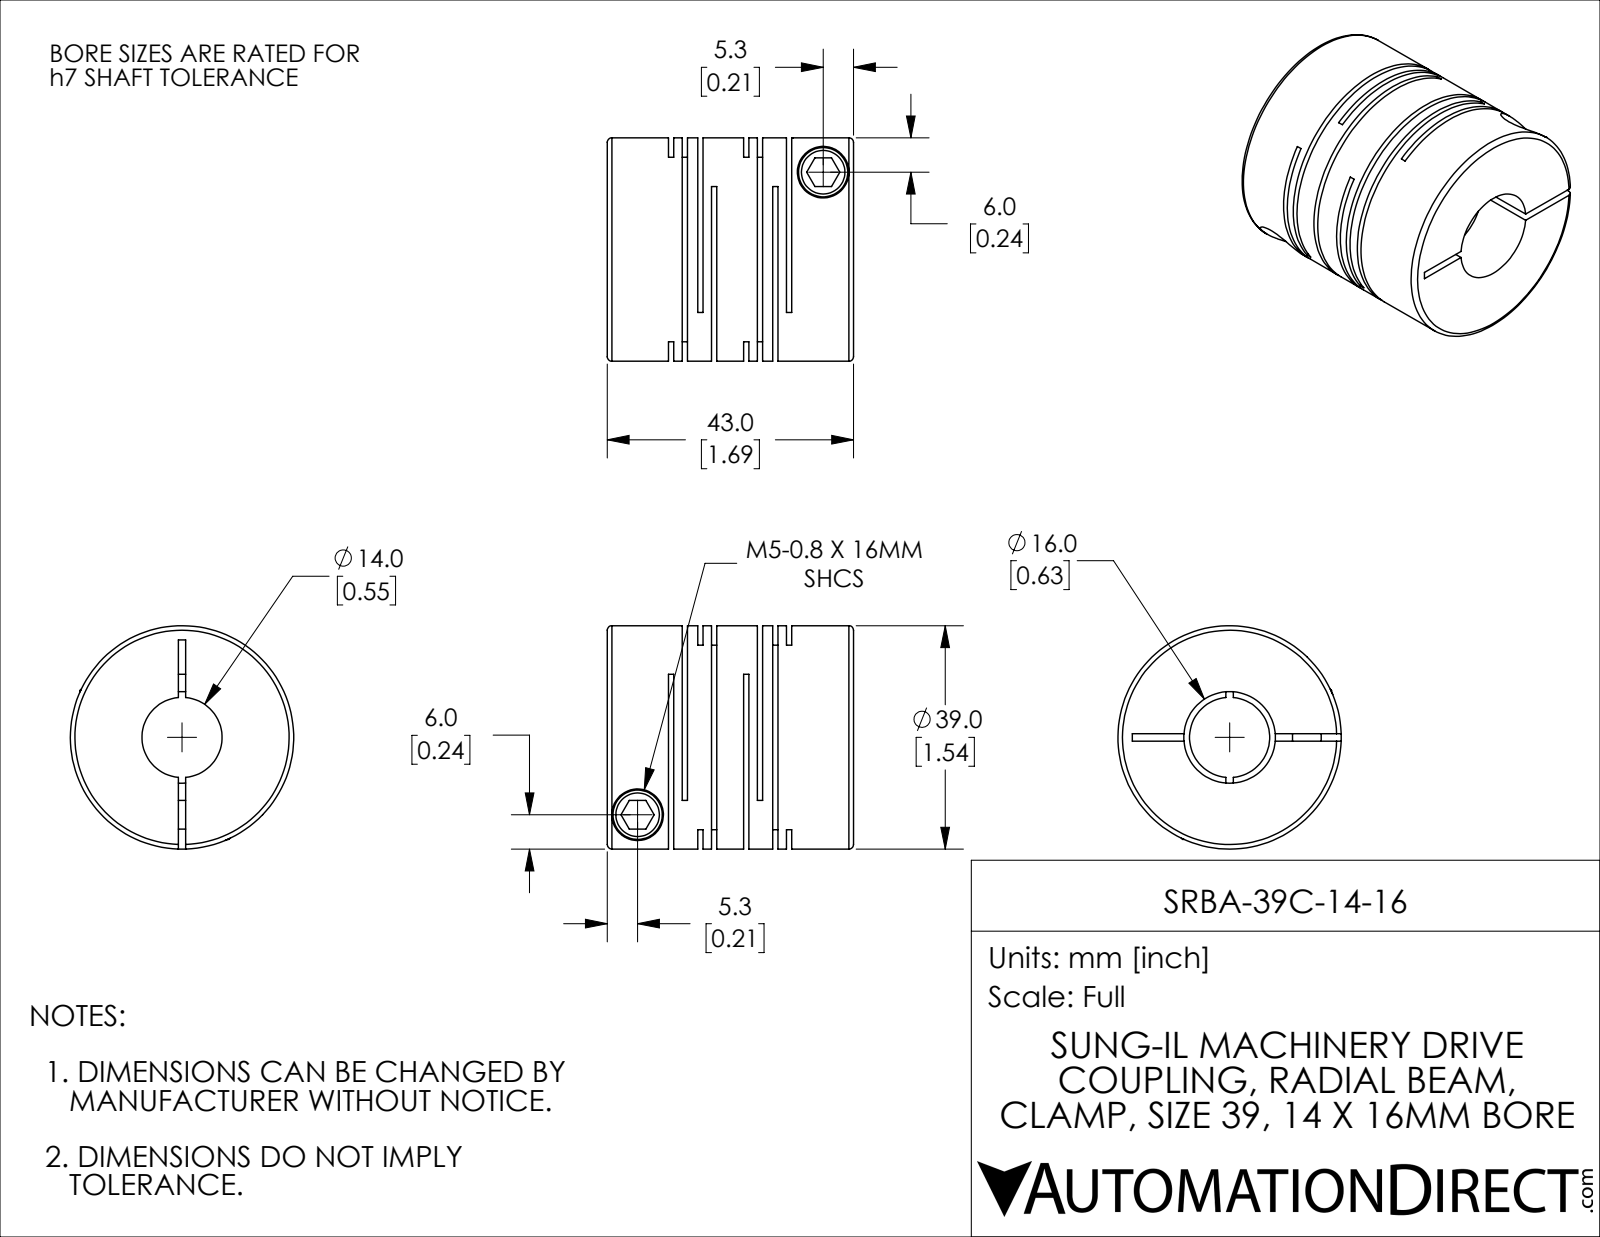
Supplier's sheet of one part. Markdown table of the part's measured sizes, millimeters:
| quantity | value |
| --- | --- |
| part name | SRBA-39C-14-16 |
| STEP written by | SolidWorks 2021 (CONFIG_CONTROL_DESIGN) |
| units | millimeters |
| bodies | 1 solid, 114 faces (60 planar, 42 cylindrical, 12 other) |
| overall size | 43 × 39 × 39 |
| volume | 35 820 mm³ |
| surface area | 23 009 mm² |
| round holes (diameter × count) | 5 × 2, 9 × 2, 14 × 1, 16 × 1 |
| round bosses / shafts (diameter × count) | 8.6 × 2, 39 × 1 |
| main face-to-face distances | 13.1, 0.92, 2.4, 5.1, 10.7, 14.02, 18.2, 3.32, 15.5, 1.48 |
